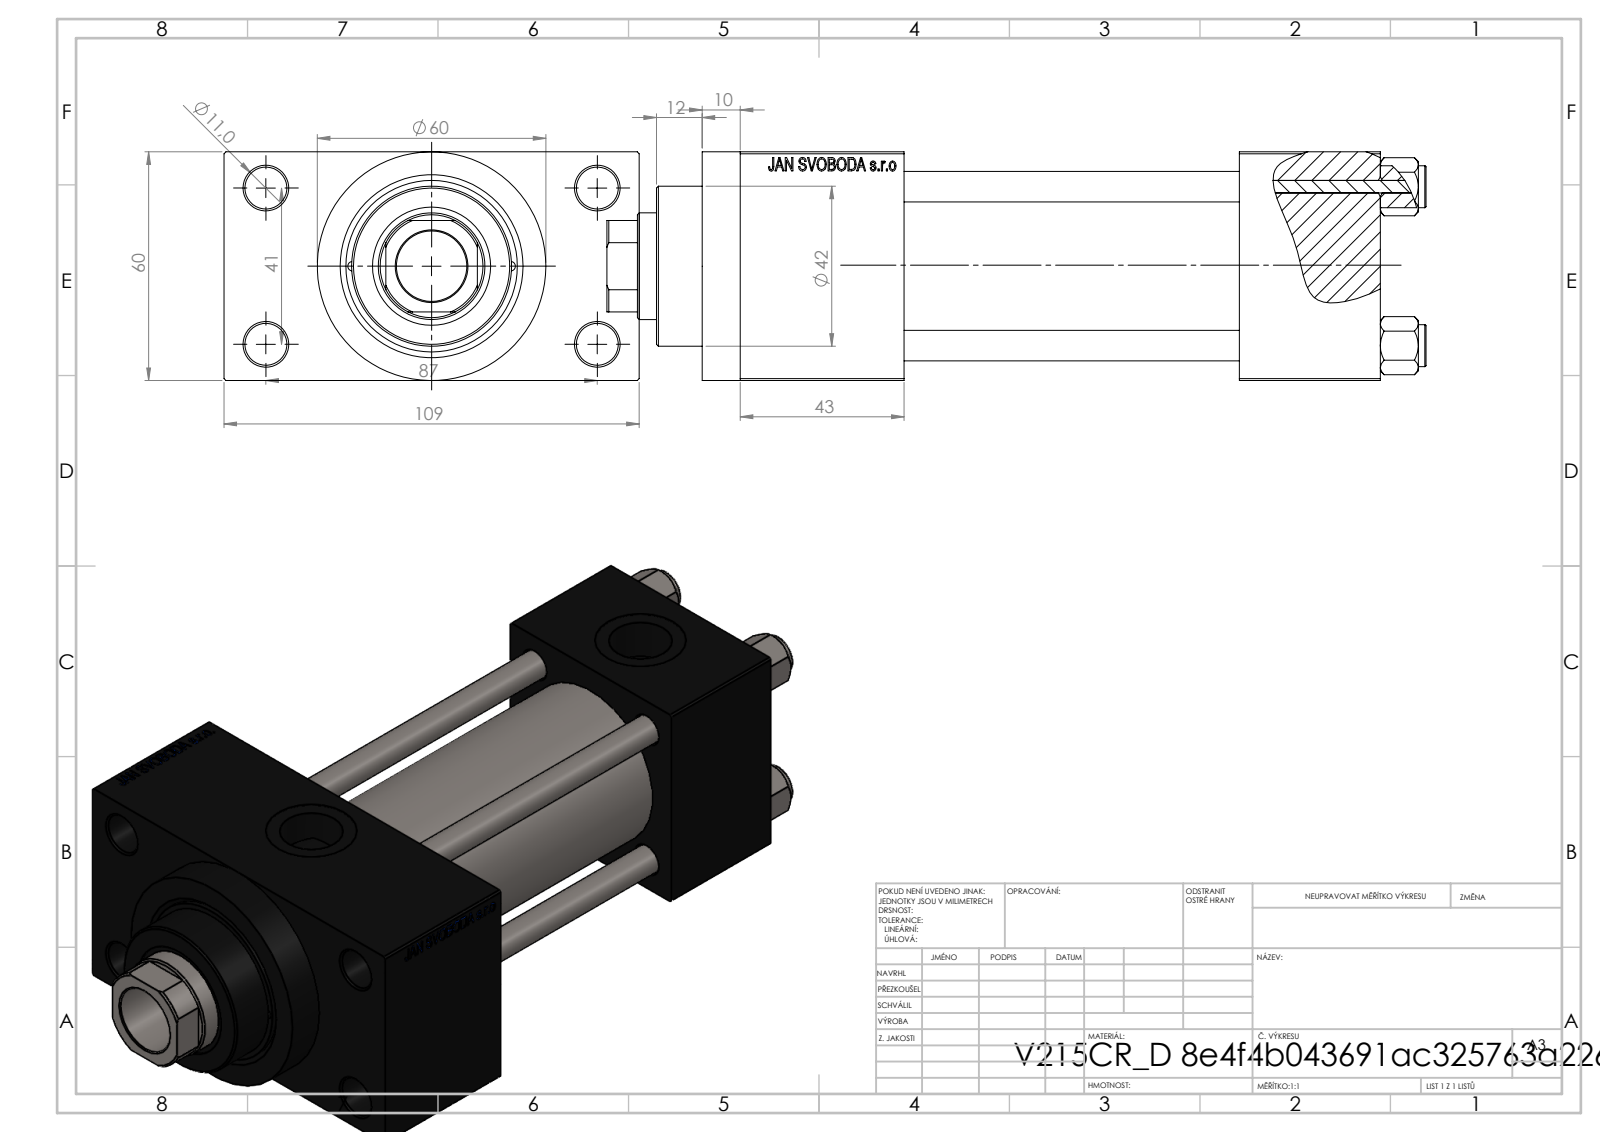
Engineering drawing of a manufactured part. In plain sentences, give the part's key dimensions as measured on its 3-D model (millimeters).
The part is named "NUT_M5_D; V215CR_VCP_D; V215CR_D_Body; V215_VC_A (+1 more)". Its 3-D file was written by "SolidWorks 2019 (CONFIG_CONTROL_DESIGN)". It is 11 solids with 1115 faces: 502 planar, 93 cylindrical and 520 other. Overall it measures 215 by 109 by 60 millimeters. Its volume is 570 571 cubic millimeters and its surface area 141 556 square millimeters. Round holes: 4 of diameter 8, 4 of diameter 11, 2 of diameter 2.5, 2 of diameter 7, 2 of diameter 16.66, 2 of diameter 24, 1 of diameter 18.5, 1 of diameter 28, 1 of diameter 31, 1 of diameter 40, 1 of diameter 45. Round bosses or shafts: 4 of diameter 11, 1 of diameter 60, 1 of diameter 46, 1 of diameter 42. Partial cylindrical surfaces (rounded edges, fillets, slot ends): 1 of radius 13.5. The main face-to-face distances are 60, 24.5, 84.5, 88, 37, 125, 168, 131, 43, 109. The hole center spacings are 20.85, 22.65, 29.49, 30.62, 41.7, 46.53, 47.15, 48.09.
